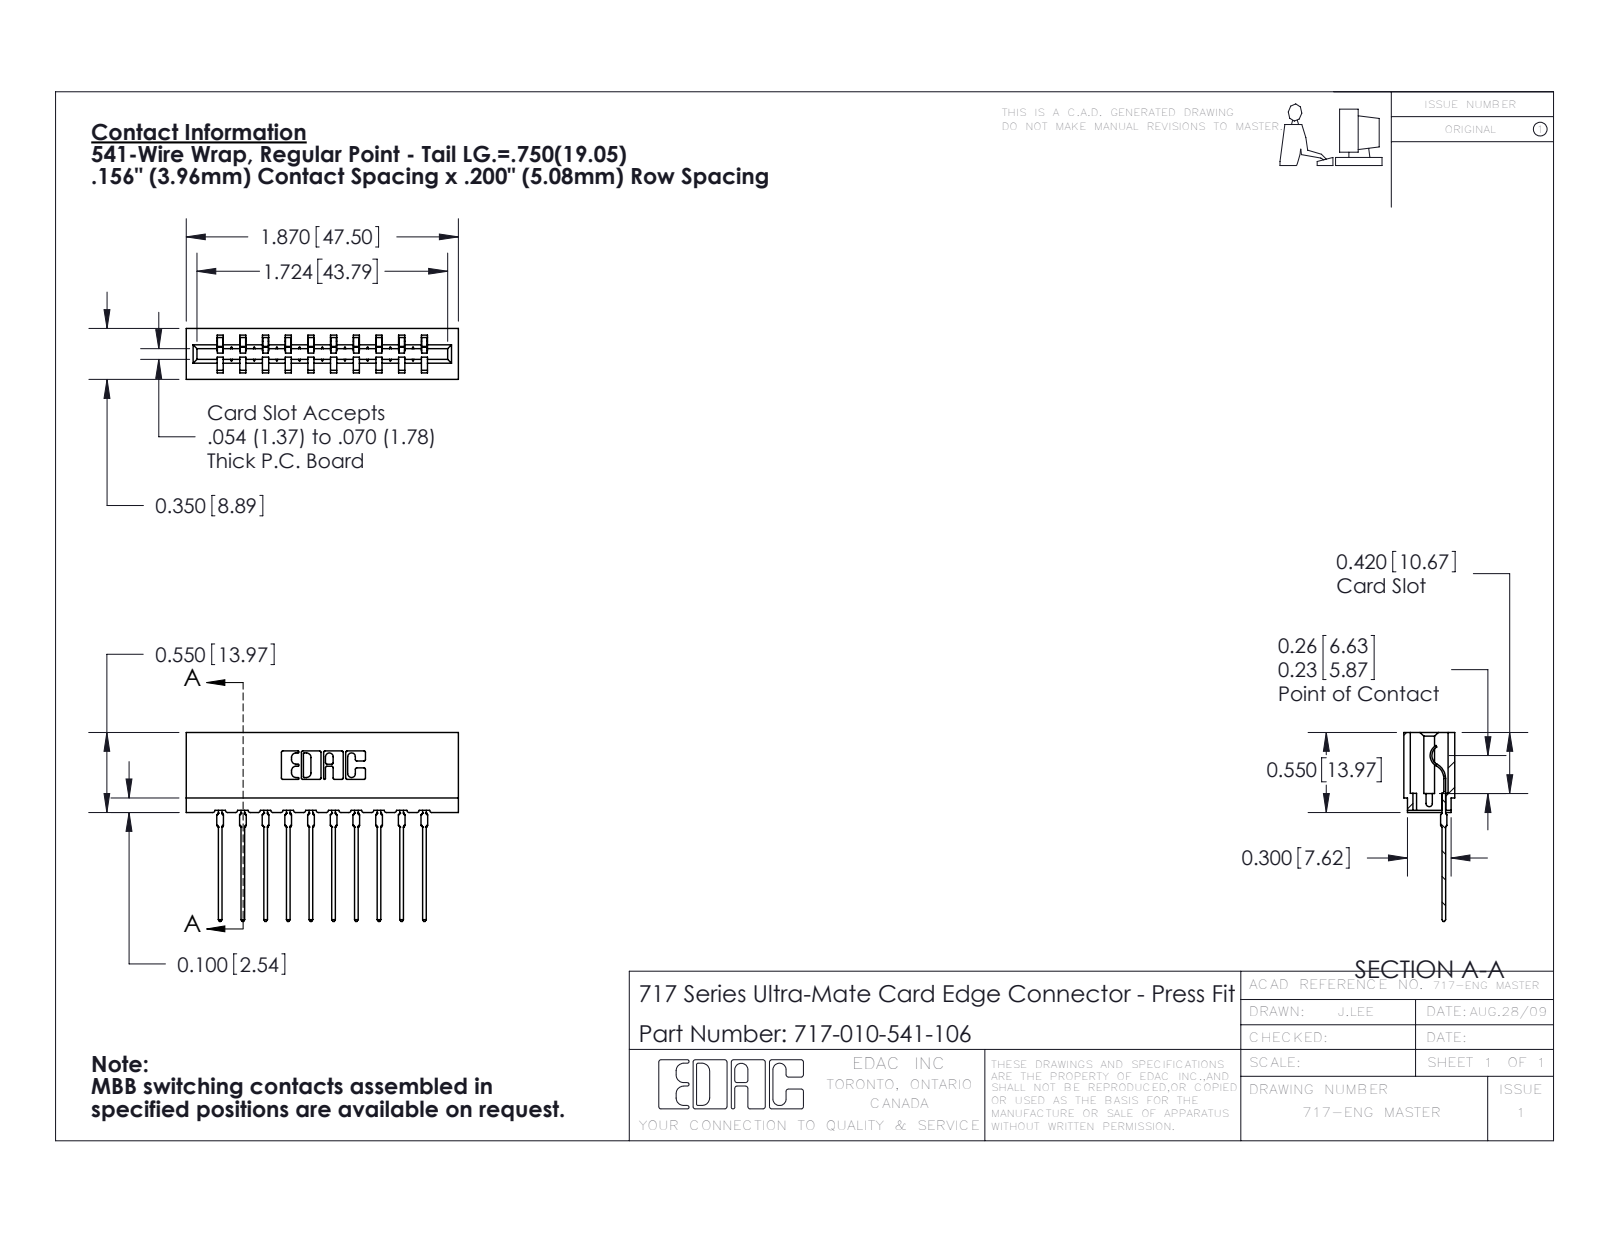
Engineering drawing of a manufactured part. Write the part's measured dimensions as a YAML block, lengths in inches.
part_name: "717 Part_Insulator Option - 06; 745-292-001_541; 717-010-541-106"
step_written_by: "SolidWorks 2016 (CONFIG_CONTROL_DESIGN)"
units: inches
bodies: {solids: 11, faces: 1224, planar: 734, cylindrical: 230, other: 260}
overall_size: [1.87, 1.299, 0.35]
volume: 0.256
surface_area: 8.929
partial_cylinders:
  - {radius: 0.01, count: 22}
  - {radius: 0.015, count: 20}
  - {radius: 0.021, count: 20}
  - {radius: 0.007, count: 6}
  - {radius: 0.031, count: 6}
  - {radius: 0.005, count: 4}
  - {radius: 0.011, count: 4}
  - {radius: 0.026, count: 3}
face_to_face_distances: [0.156, 0.212, 0.138, 0.624, 0.35, 0.198, 0.468, 0.312, 0.354, 0.312]
